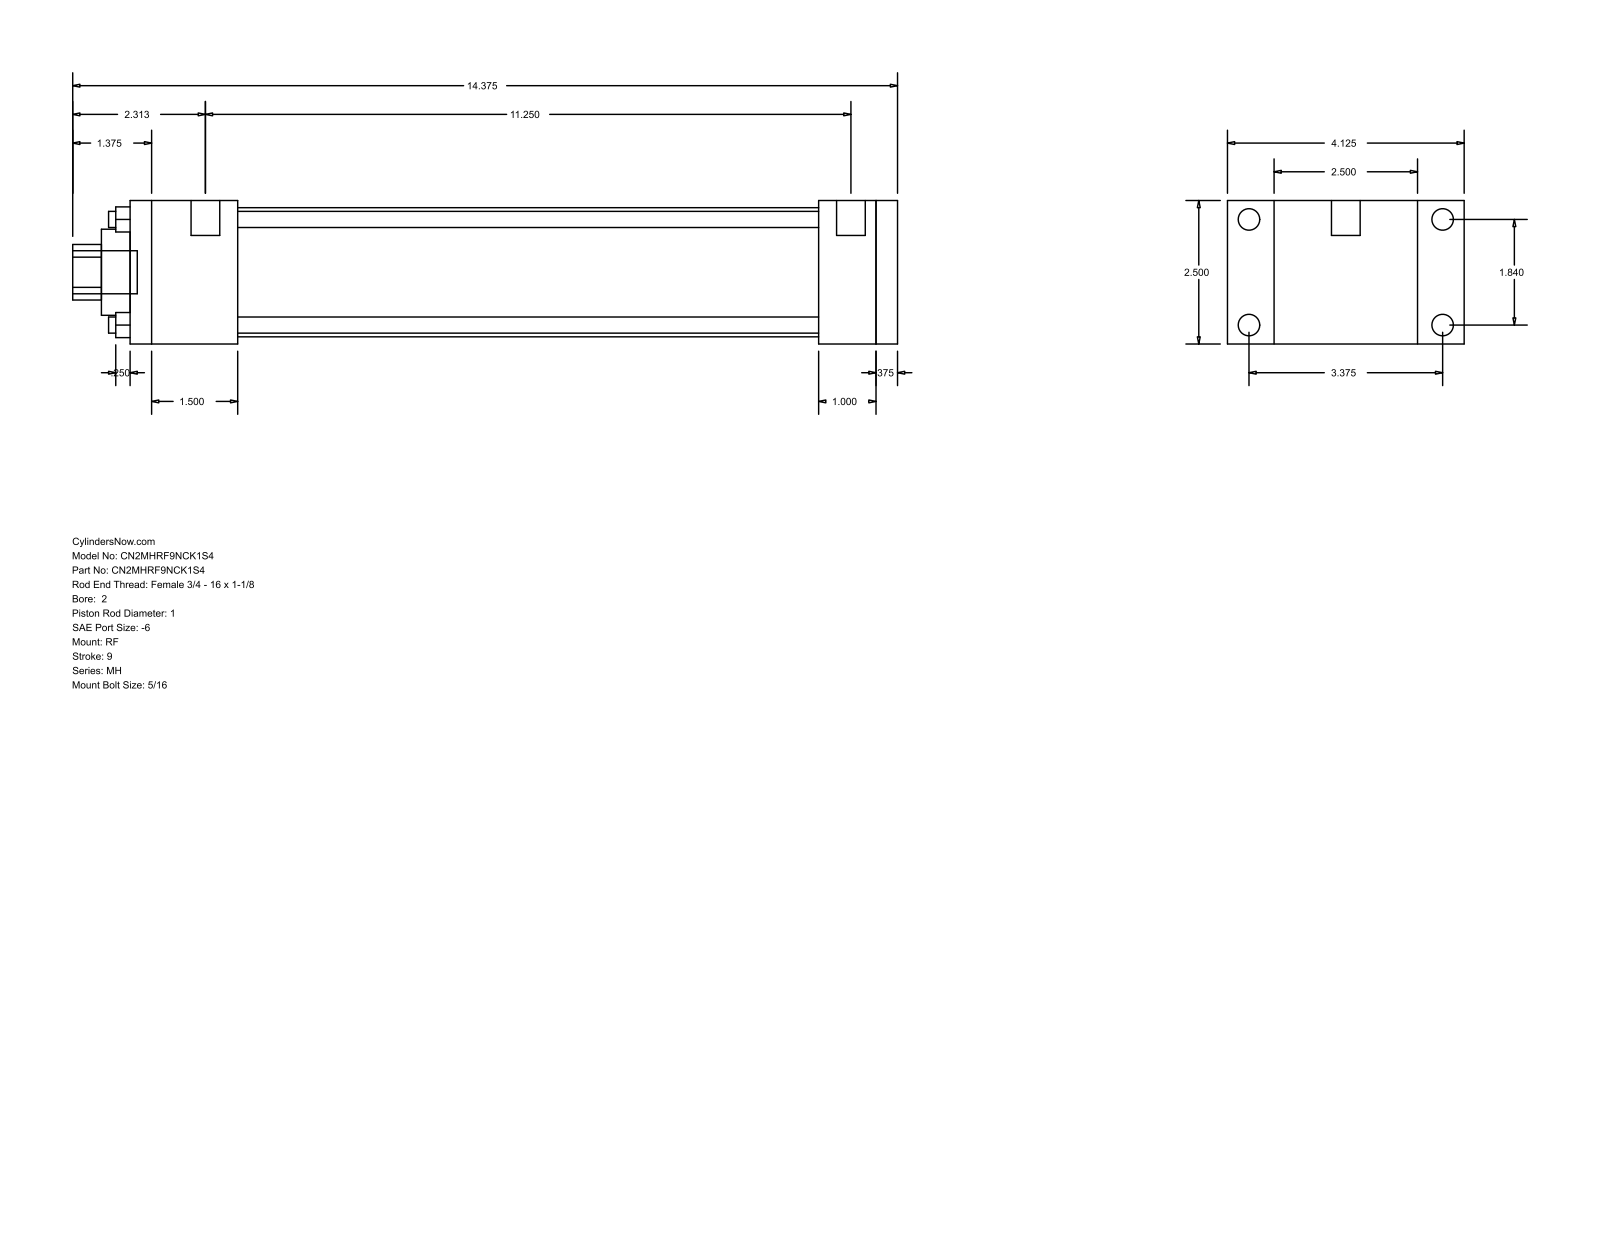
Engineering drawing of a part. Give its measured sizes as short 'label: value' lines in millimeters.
name: MH_RF__0200_1
written by: GSSL Pune (CONFIG_CONTROL_DESIGN)
unit: mm
bodies: 0 solids, 92 faces (64 planar, 28 cylindrical, 0 other)
size: 365.12 × 104.78 × 63.5
holes: 4× ⌀7.14, 1× ⌀25.4, 1× ⌀38.1, 1× ⌀57.15
bosses: 4× ⌀9.53, 4× ⌀5.56, 2× ⌀12.7, 1× ⌀19.05
rounds: 1× R12.29
face distances: 63.5, 9.52, 339.72, 330.2, 20.64, 25.4, 47.63, 304.8, 257.17, 282.57
hole spacings: 33.05, 46.74, 66.1
